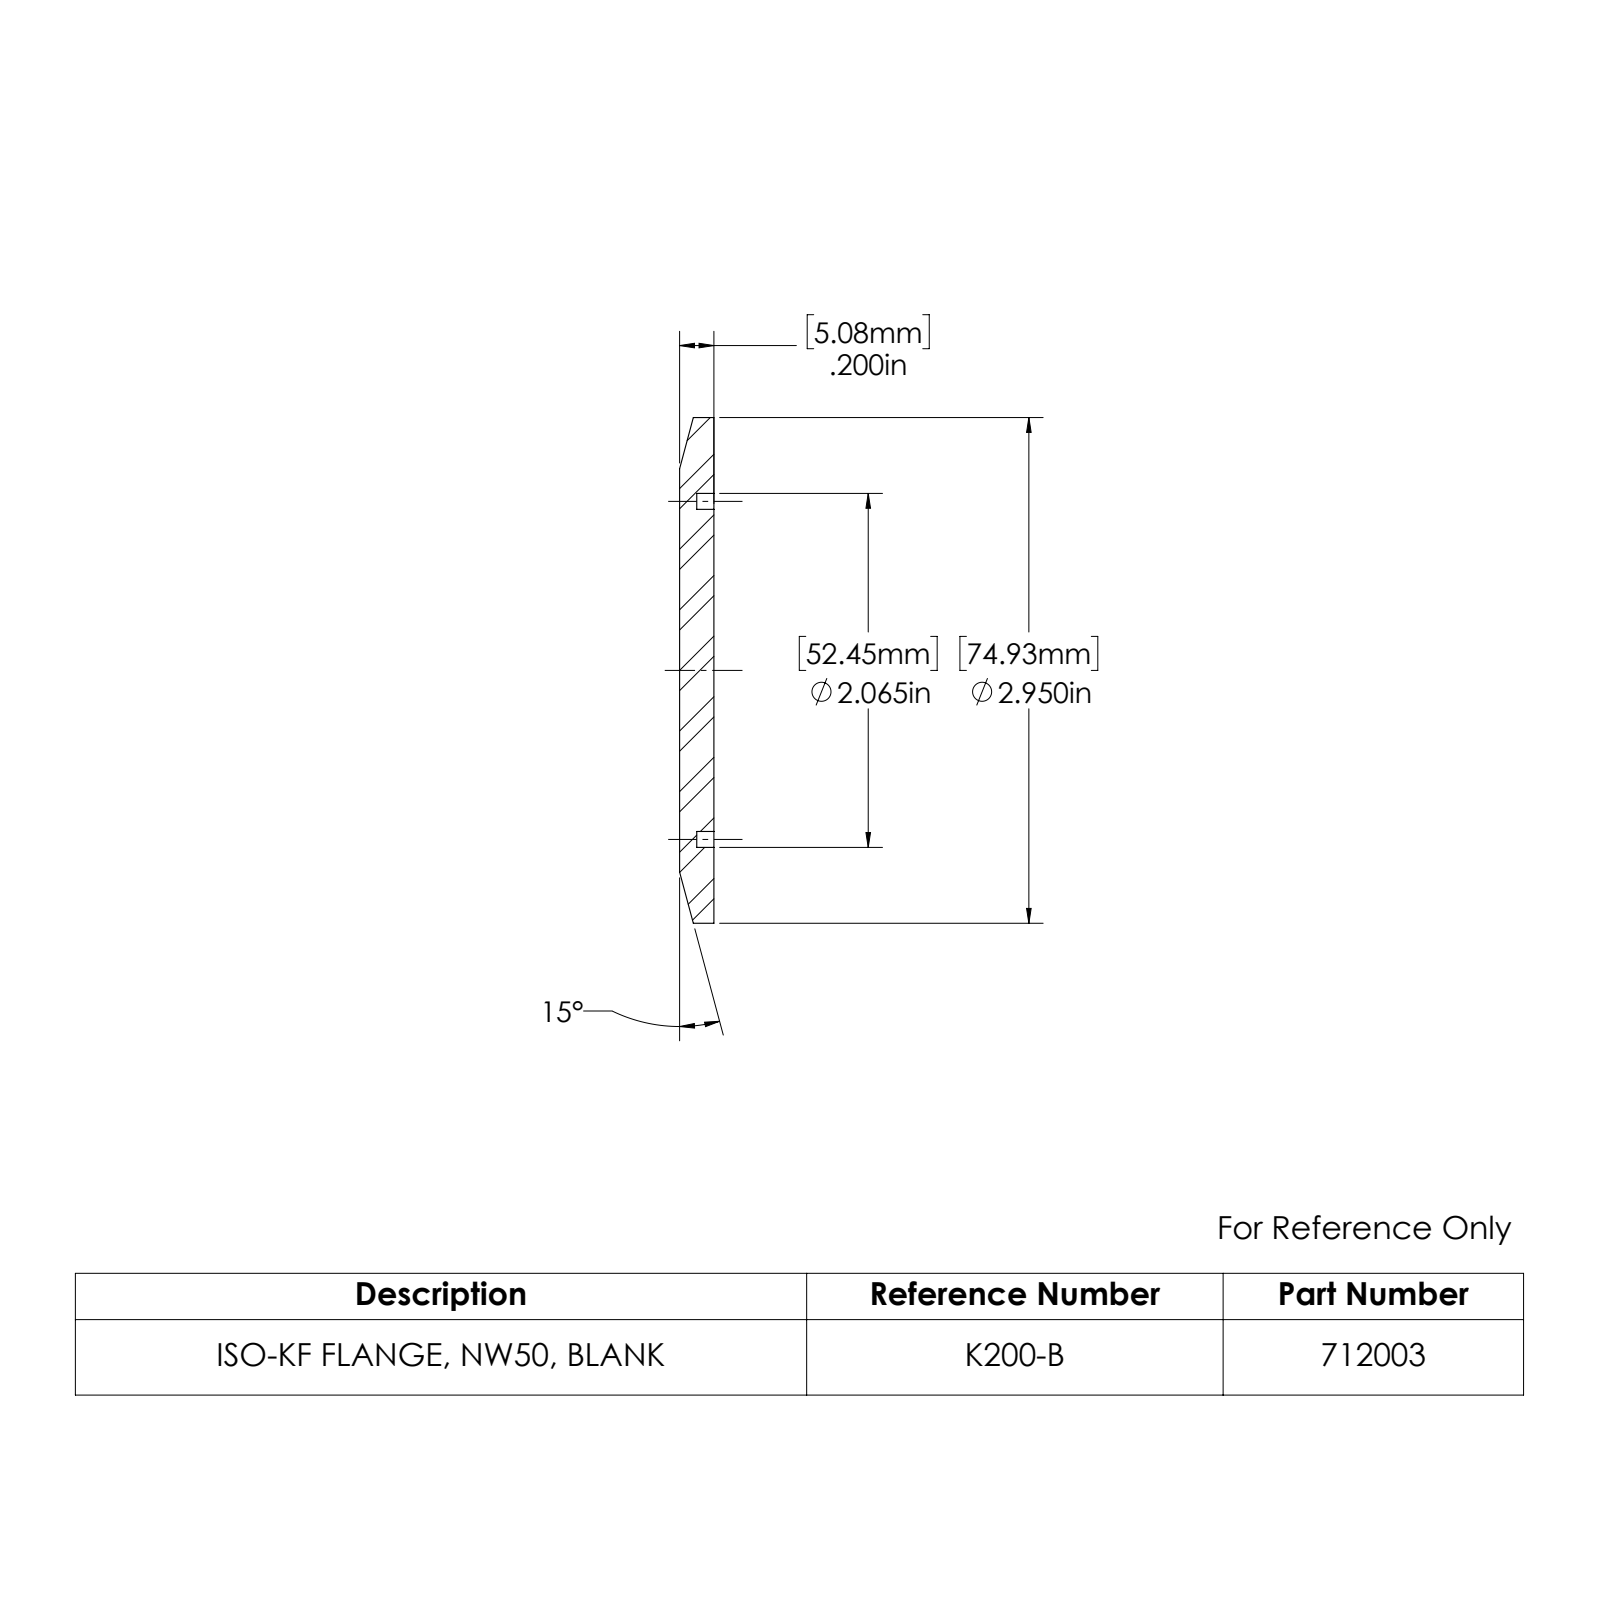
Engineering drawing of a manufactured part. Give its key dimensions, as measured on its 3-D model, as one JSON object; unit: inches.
{"part_name": "712003", "step_written_by": "SolidWorks 2022 (AUTOMOTIVE_DESIGN)", "units": "inches", "bodies": {"solids": 1, "faces": 12, "planar": 4, "cylindrical": 6, "other": 2}, "overall_size": [2.95, 2.95, 0.2], "volume_in3": 1.206, "surface_area_in2": 16.11, "round_holes": [[2.065, 1]], "round_bosses_or_shafts": [[2.95, 1], [1.879, 1]], "face_to_face_distances": [0.2, 0.1]}
